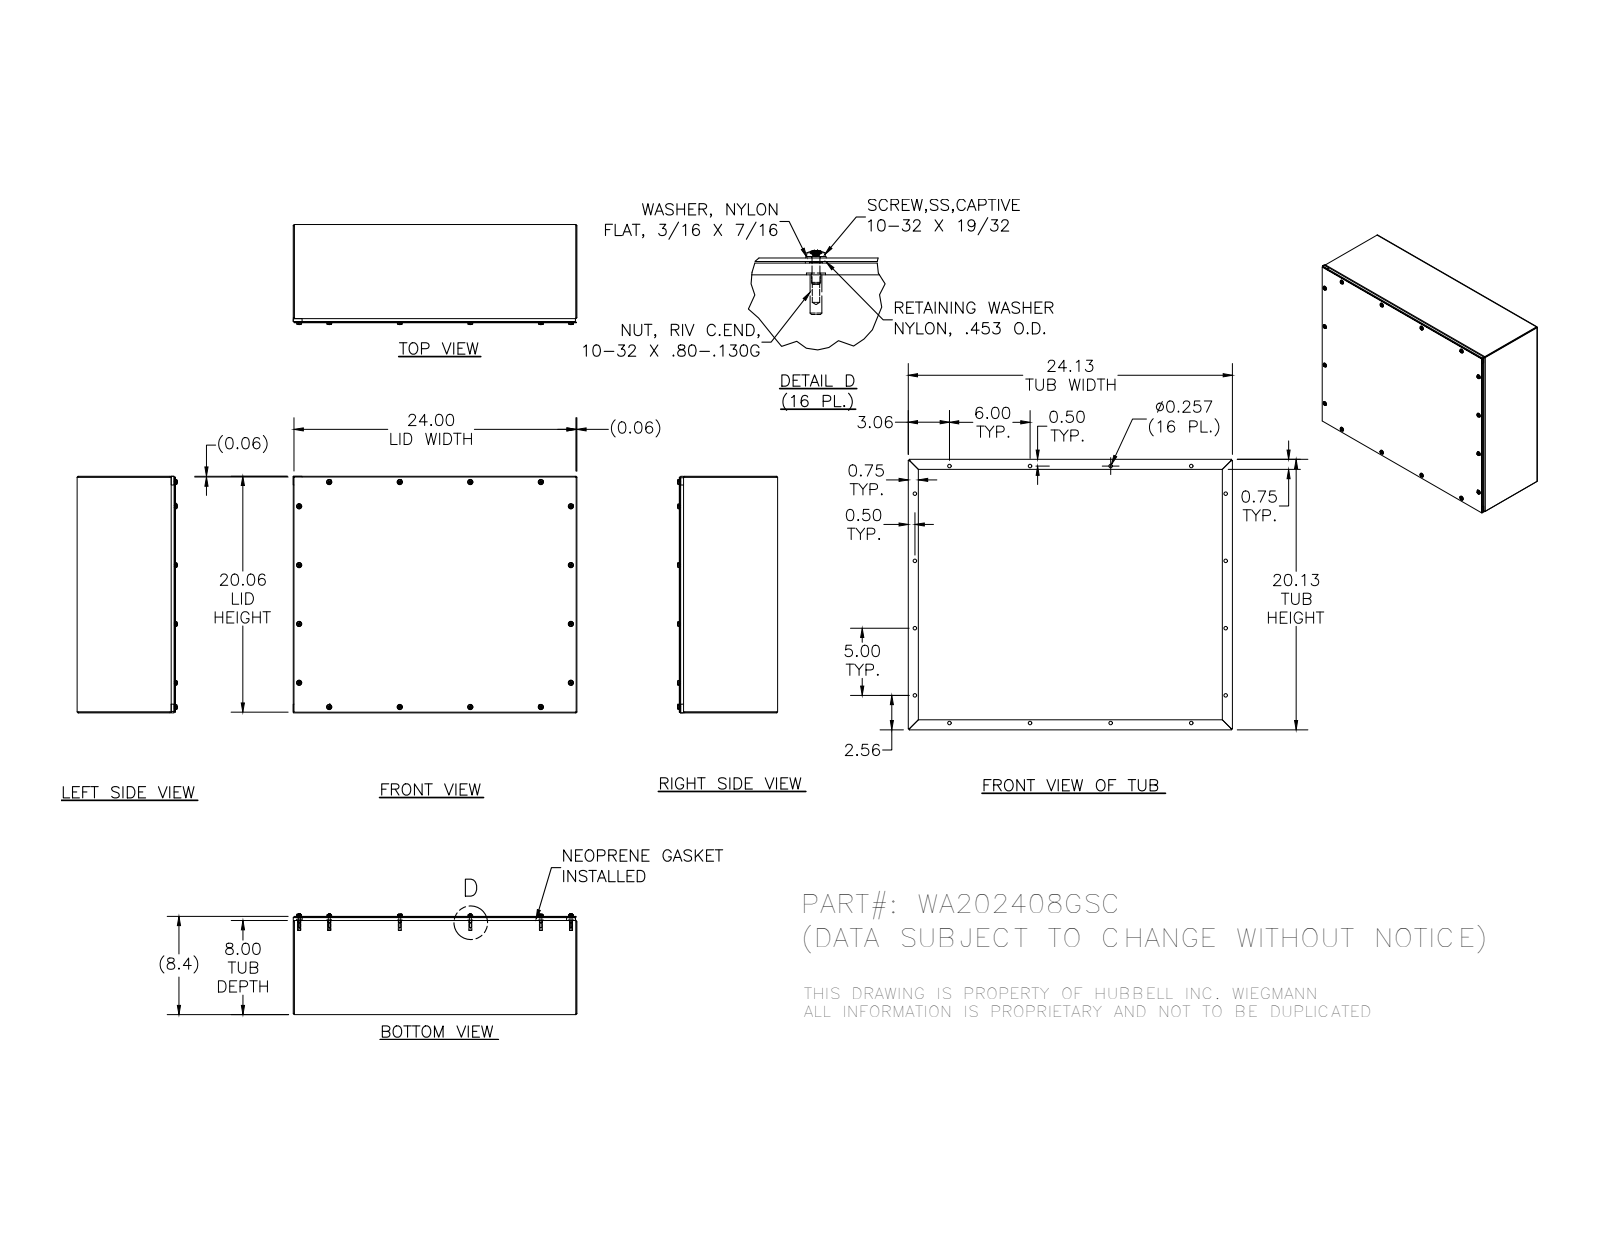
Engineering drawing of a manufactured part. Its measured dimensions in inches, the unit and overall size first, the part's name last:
Units: inches
Overall size (bounding box): 24.125 × 20.125 × 8.511
Round holes (diameter × count): ⌀0.188 ×16, ⌀0.257 ×16, ⌀0.278 ×16, ⌀0.281 ×16, ⌀0.156 ×15, ⌀0.196 ×15
Round bosses / shafts (diameter × count): ⌀0.453 ×16, ⌀0.437 ×16, ⌀0.167 ×16, ⌀0.406 ×15, ⌀0.248 ×15
Partial cylindrical surfaces — rounded edges, fillets, slot ends (radius × count): R0.089 ×16, R0.031 ×8, R0.105 ×8
Main face-to-face distances: 0.074, 8.282, 8.356, 8.208, 24.051, 20.051, 19.977, 0.074, 20.051, 20.125
Hole centre spacings: 6, 5, 12, 20.044, 10, 14.793, 3.289, 8.807
Volume: 140.5 in³ · Surface area: 3 625 in²
Bodies: 69 solids, 1646 faces (766 planar, 432 cylindrical, 448 other)
Part name (STEP PRODUCT): 39035; WA202408GSC; 39077; WA202408GSCBKP (+3 more)
STEP written by: SolidWorks 2014 (AUTOMOTIVE_DESIGN)
